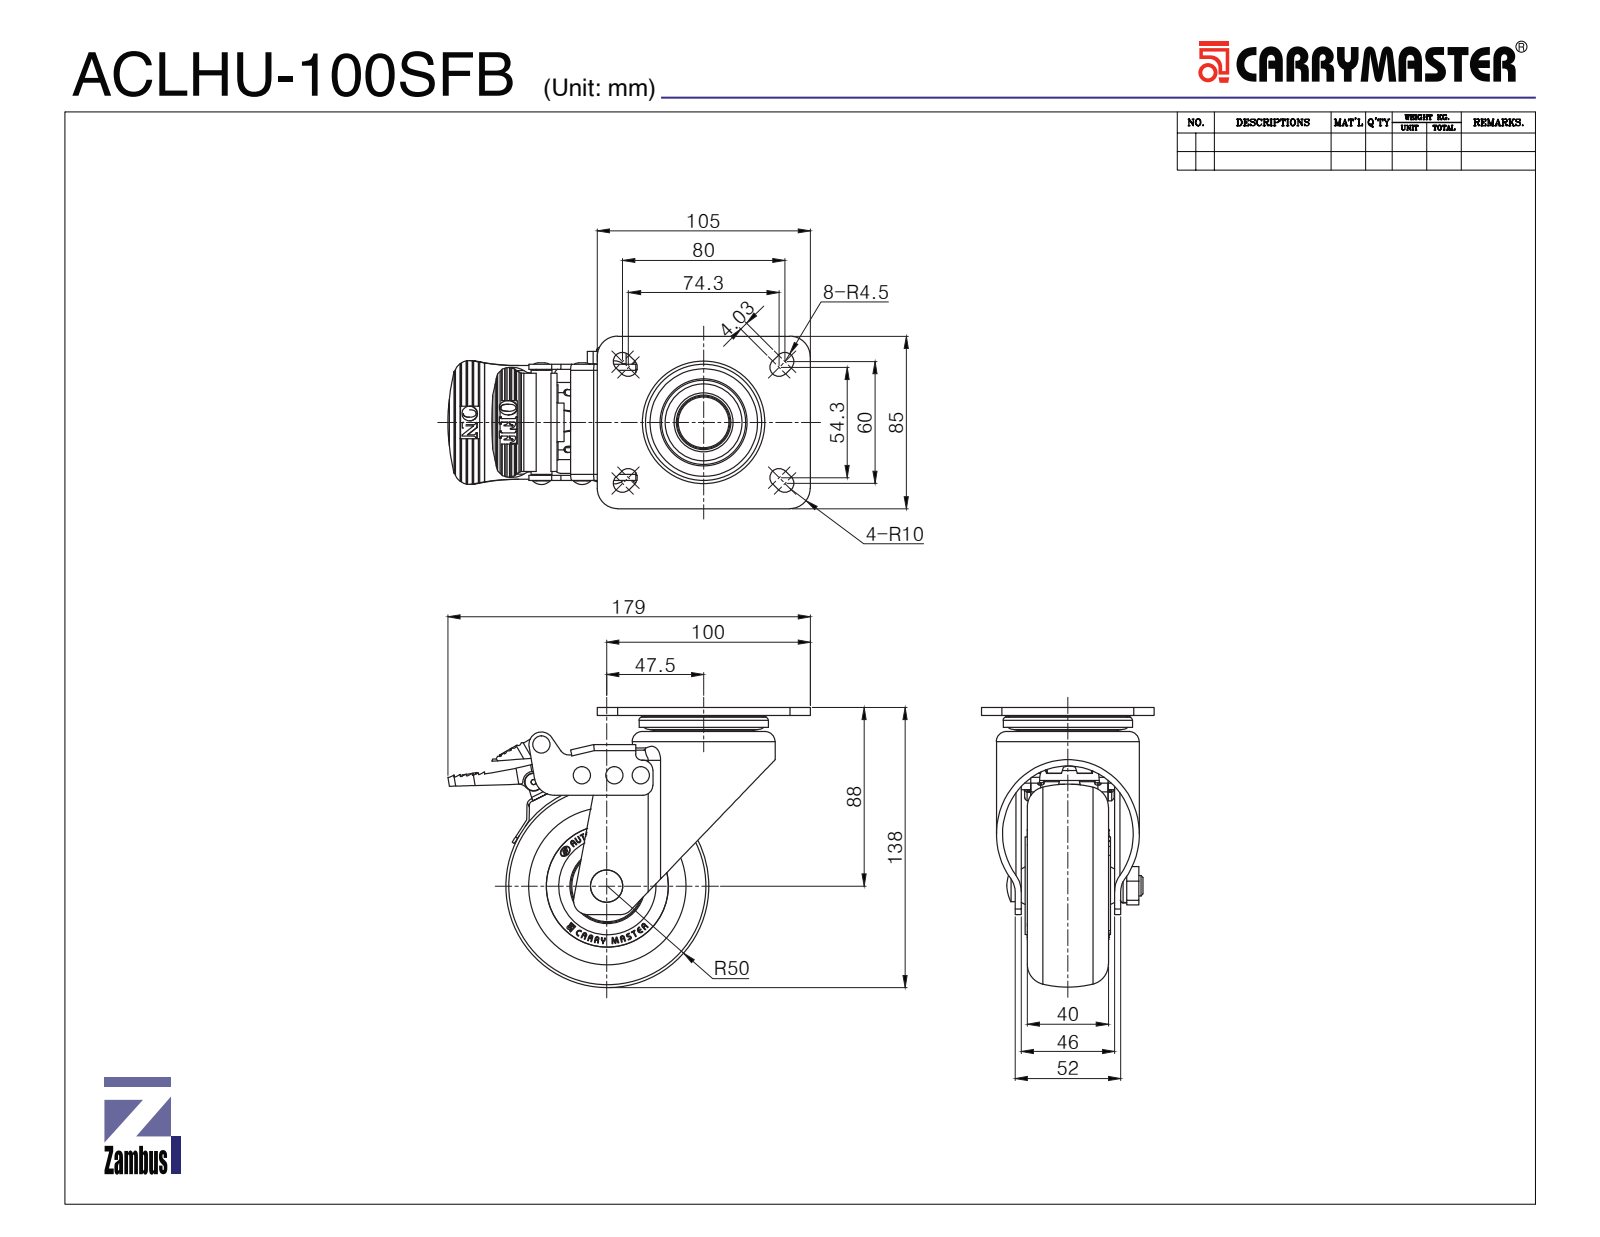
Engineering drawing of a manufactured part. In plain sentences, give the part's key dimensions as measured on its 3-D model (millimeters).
The part is named "ACLMU-100SFB". Its 3-D file was written by "SolidWorks 2015 (CONFIG_CONTROL_DESIGN)". It is 40 solids with 2382 faces: 1269 planar, 513 cylindrical and 600 other. Overall it measures 178.55 by 138 by 85 millimeters. Its volume is 464 236 cubic millimeters and its surface area 175 203 square millimeters. Round holes: 2 of diameter 1.7, 2 of diameter 3.5, 2 of diameter 4.3, 2 of diameter 5, 1 of diameter 2.5, 1 of diameter 2.6, 1 of diameter 4, 1 of diameter 5.2, 1 of diameter 5.3, 1 of diameter 8.5, 1 of diameter 10, 1 of diameter 12. Round bosses or shafts: 4 of diameter 4.9, 2 of diameter 9, 2 of diameter 6.9, 2 of diameter 0.65, 1 of diameter 80, 1 of diameter 70.42, 1 of diameter 63.7, 1 of diameter 60.5. Partial cylindrical surfaces (rounded edges, fillets, slot ends): 41 of radius 1, 24 of radius 3, 15 of radius 1.5, 8 of radius 4.5, 7 of radius 5, 5 of radius 0.5, 5 of radius 2, 5 of radius 10. The main face-to-face distances are 3, 4, 46, 6, 2.5, 43, 2, 5, 49, 1. The hole center spacings are 27.92, 0.46, 9.31, 9.7, 12.81, 13, 16, 16.66.
